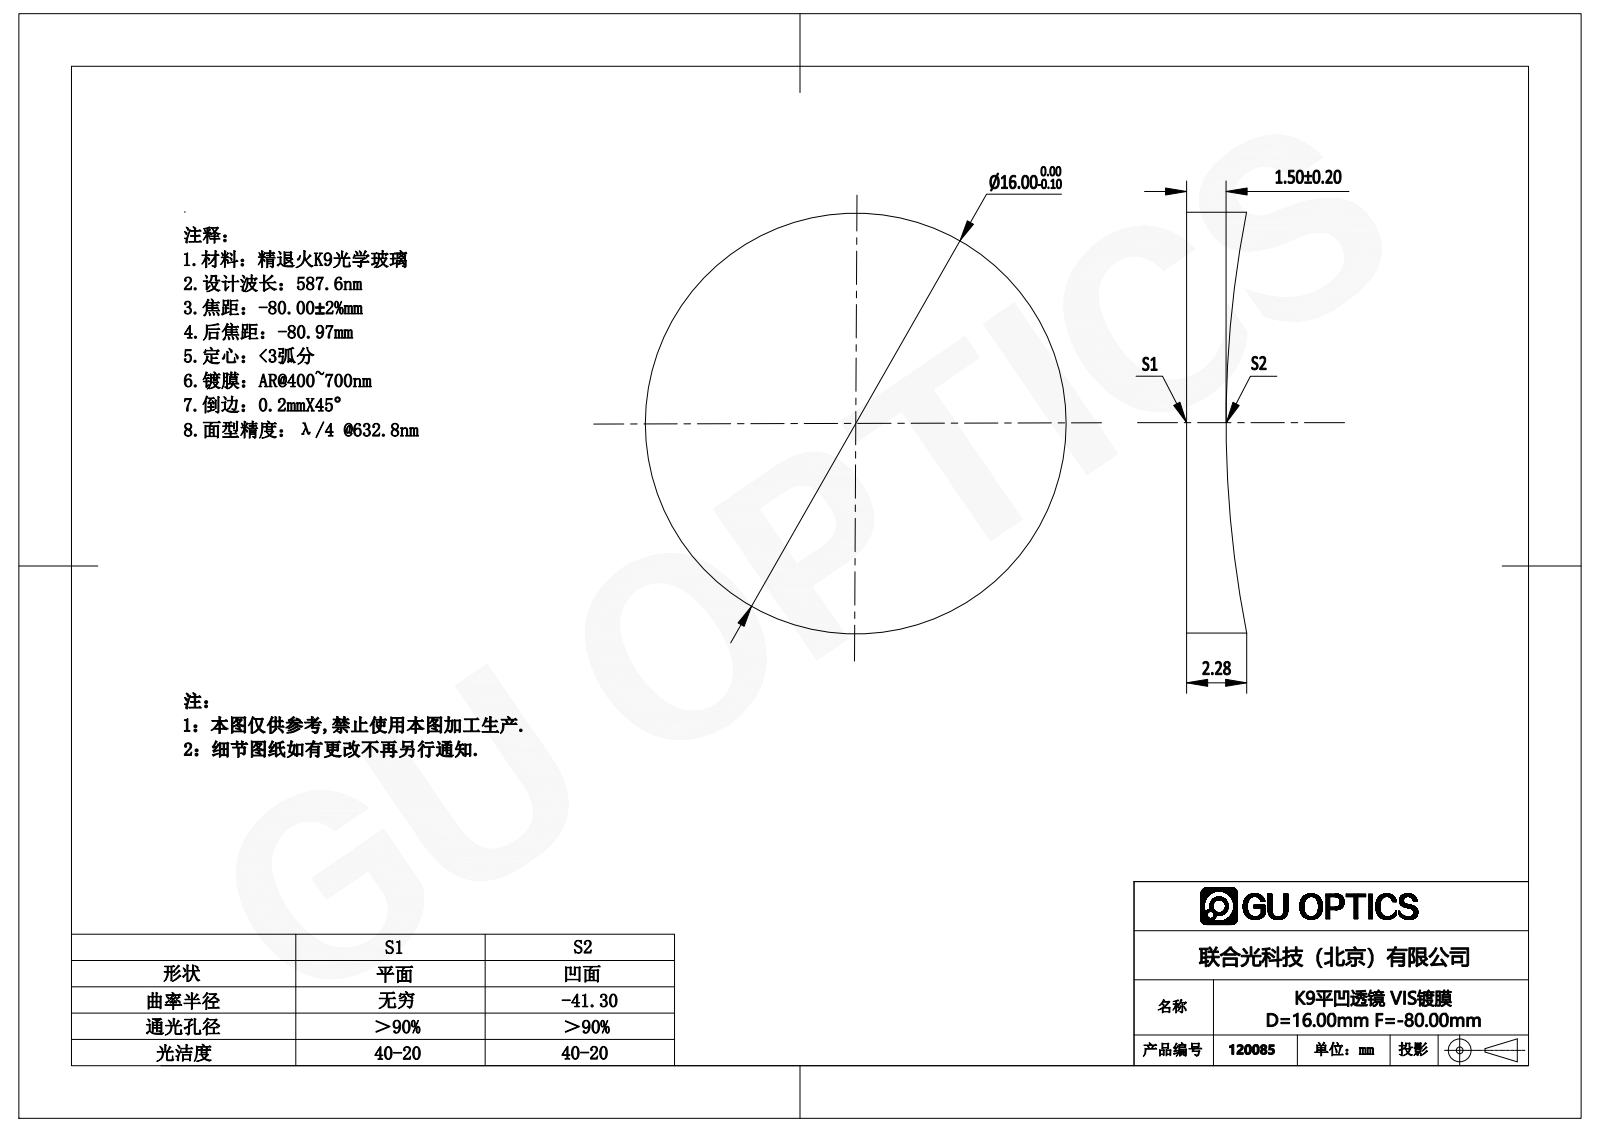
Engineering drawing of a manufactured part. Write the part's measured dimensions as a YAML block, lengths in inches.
part_name: "120025"
step_written_by: "SolidWorks 2016 (AUTOMOTIVE_DESIGN)"
units: inches
bodies: {solids: 1, faces: 5, planar: 1, cylindrical: 2, other: 2}
overall_size: [0.63, 0.63, 0.09]
volume: 0.023
surface_area: 0.804
round_bosses_or_shafts:
  - {diameter: 0.63, count: 1}
